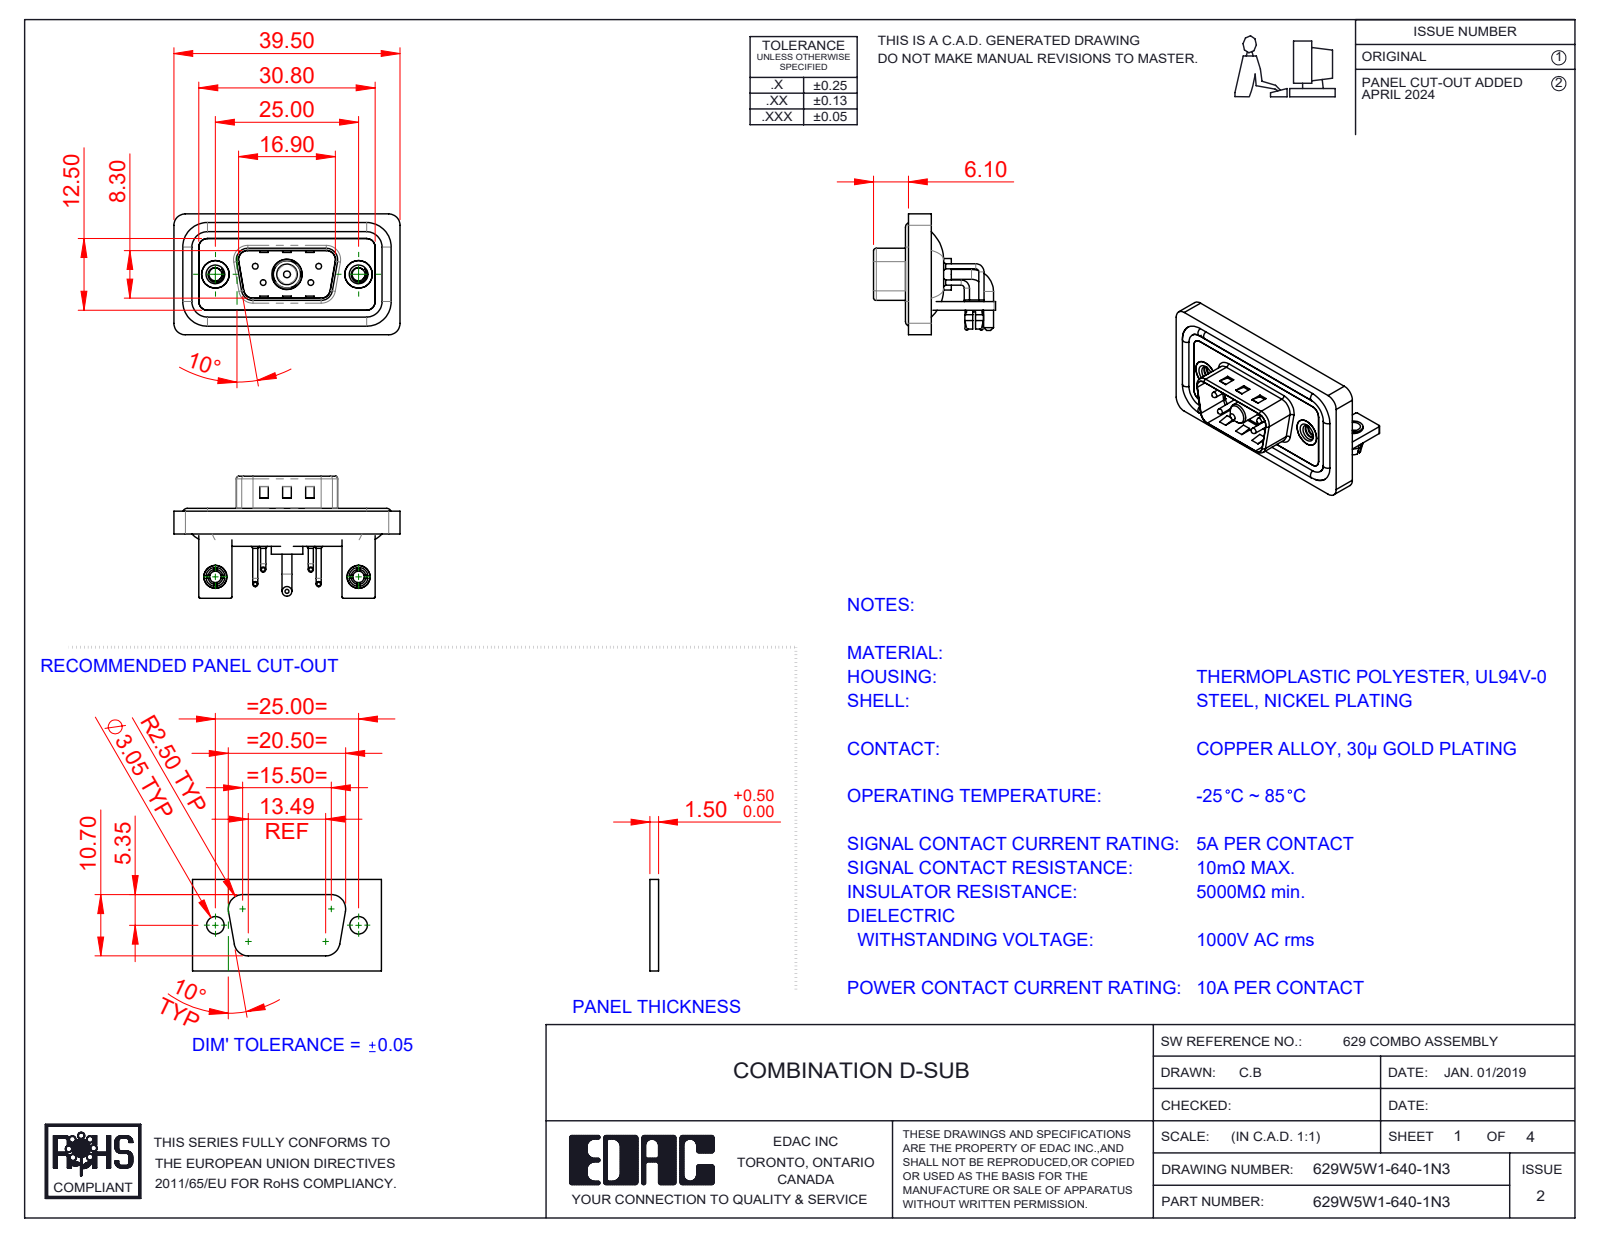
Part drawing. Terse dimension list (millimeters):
name: 629Combo Stabilizer Bracket; 629Combo Waterproof Housing_09 Contacts; 629Combo Threaded Rivet_3; 629Combo Shell Rear_09 Contacts (+7 more)
written by: SolidWorks 2023 (CONFIG_CONTROL_DESIGN)
unit: mm
bodies: 17 solids, 1026 faces (479 planar, 395 cylindrical, 152 other)
size: 39.5 × 21.3 × 21.1
volume: 4 732 mm³; area: 7 910 mm²
holes: 6× ⌀2, 4× ⌀0.75, 4× ⌀1.6, 2× ⌀2.26, 2× ⌀2.5, 2× ⌀3.2, 2× ⌀4, 2× ⌀4.8, 2× ⌀5, 1× ⌀4.85, 1× ⌀5.3
bosses: 8× ⌀0.9, 4× ⌀1.6, 4× ⌀1.5, 4× ⌀1, 4× ⌀0.65, 2× ⌀4.9, 2× ⌀4, 2× ⌀3.4
rounds: 19× R2, 18× R1.5, 16× R0.25, 9× R0.5, 8× R1.6, 4× R0.6, 4× R0.65, 4× R0.9
face distances: 0.4, 1.5, 0.8, 2.9, 1.1, 2.1, 1.2, 1.6, 2.5, 3.7
hole spacings: 3.16, 5.72, 7.1, 12.5, 18.1, 25, 4.39, 4.4
